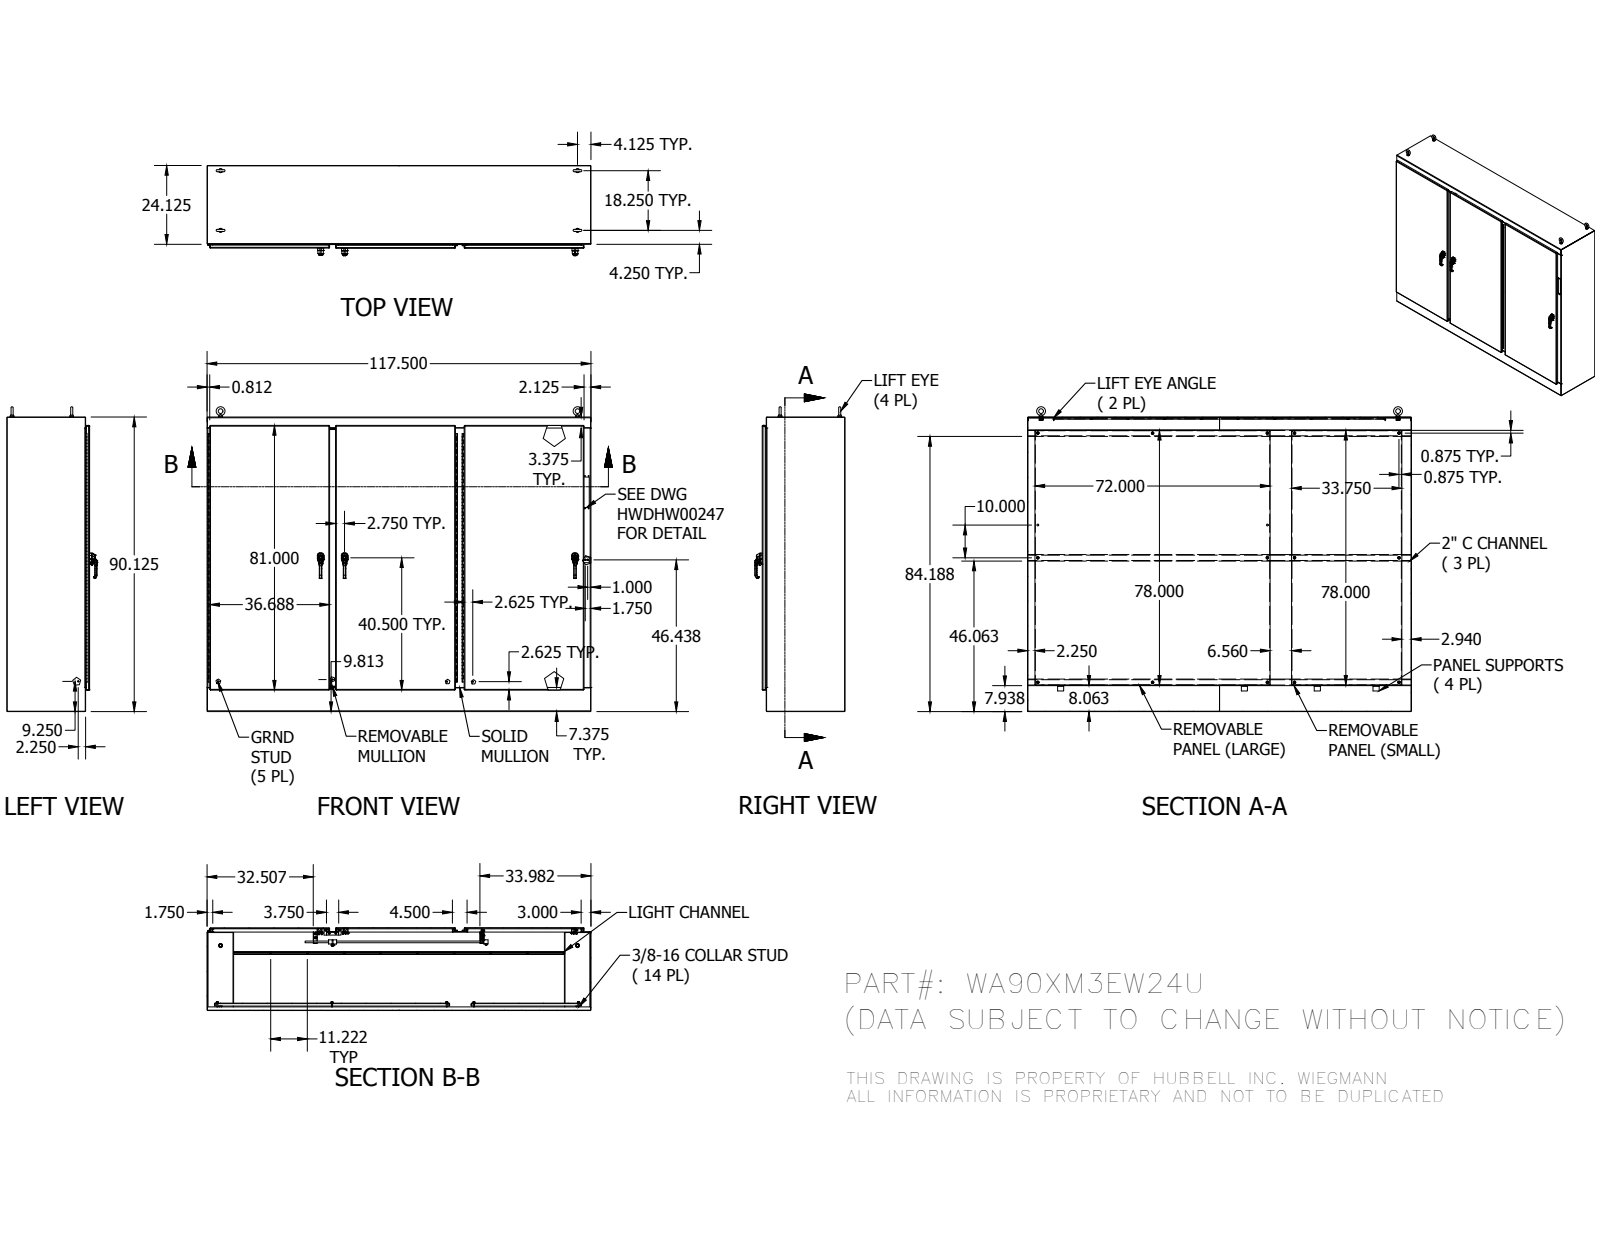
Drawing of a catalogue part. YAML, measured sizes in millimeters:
part_name: "WAXM3EW24U_TOP; HFW3025; 316298; 349132 (+8 more)"
step_written_by: "Autodesk Inventor 2014 (AUTOMOTIVE_DESIGN)"
units: millimeters
bodies: {solids: 335, faces: 12896, planar: 5991, cylindrical: 4144, other: 2761}
overall_size: [2984.5, 2368.49, 701.13]
volume: 93740000
surface_area: 59110000
round_holes:
  - {diameter: 6.35, count: 27}
  - {diameter: 9.52, count: 26}
  - {diameter: 7.02, count: 20}
  - {diameter: 14.29, count: 16}
  - {diameter: 7.8, count: 14}
  - {diameter: 5.08, count: 12}
  - {diameter: 4.83, count: 10}
  - {diameter: 7.14, count: 10}
  - {diameter: 7.33, count: 10}
  - {diameter: 8.51, count: 10}
  - {diameter: 9.65, count: 10}
  - {diameter: 5.4, count: 9}
round_bosses_or_shafts:
  - {diameter: 8.38, count: 27}
  - {diameter: 6.35, count: 25}
  - {diameter: 15.88, count: 21}
  - {diameter: 9.52, count: 17}
  - {diameter: 8.56, count: 15}
  - {diameter: 14.29, count: 13}
  - {diameter: 25.4, count: 10}
  - {diameter: 12.7, count: 10}
partial_cylinders:
  - {radius: 0.5, count: 524}
  - {radius: 0.3, count: 322}
  - {radius: 0.51, count: 240}
  - {radius: 0.47, count: 63}
  - {radius: 1.27, count: 52}
  - {radius: 1.59, count: 48}
  - {radius: 2, count: 41}
  - {radius: 1, count: 33}
face_to_face_distances: [3.17, 640.83, 3.18, 50.8, 53.97, 57.15, 53.98, 1.59, 637.66, 586.86]
hole_center_spacings: [1.6, 1847.53, 285.04, 1.59, 570.08, 1838, 855.12, 968.37]
